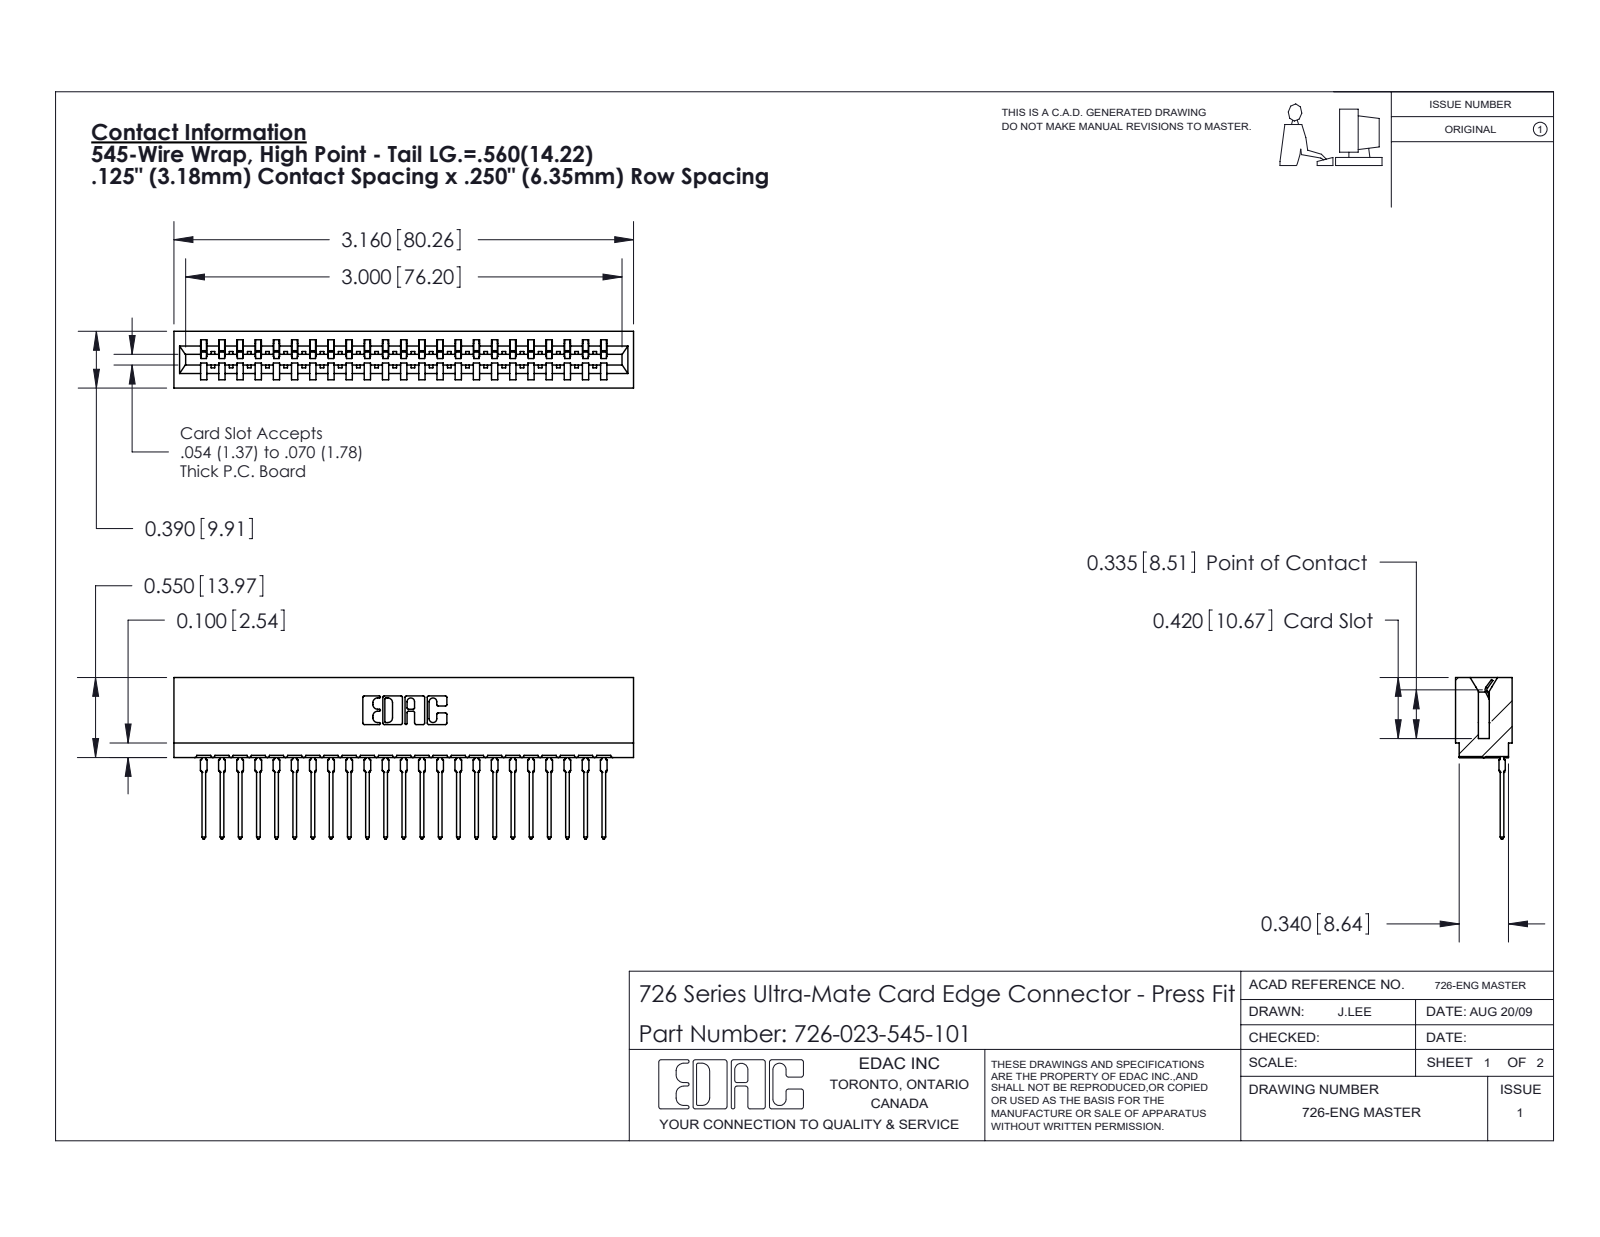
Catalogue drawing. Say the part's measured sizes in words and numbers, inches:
The part is named "726 Part_.515 Slot Depth - 01; 746-292-001_545; 726-023-545-101". Its 3-D file was written by "SolidWorks 2020 (CONFIG_CONTROL_DESIGN)". It is 24 solids with 2581 faces: 1504 planar, 479 cylindrical and 598 other. Overall it measures 3.16 by 1.109 by 0.39 inches. Its volume is 0.448 cubic inches and its surface area 17.43 square inches. Partial cylindrical surfaces (rounded edges, fillets, slot ends): 46 of radius 0.021, 24 of radius 0.015, 22 of radius 0.01, 6 of radius 0.007, 6 of radius 0.031, 4 of radius 0.005, 4 of radius 0.011, 3 of radius 0.026. The main face-to-face distances are 0.057, 0.333, 0.39, 0.025, 0.307, 0.25, 0.75, 0.083, 0.042, 0.5.
